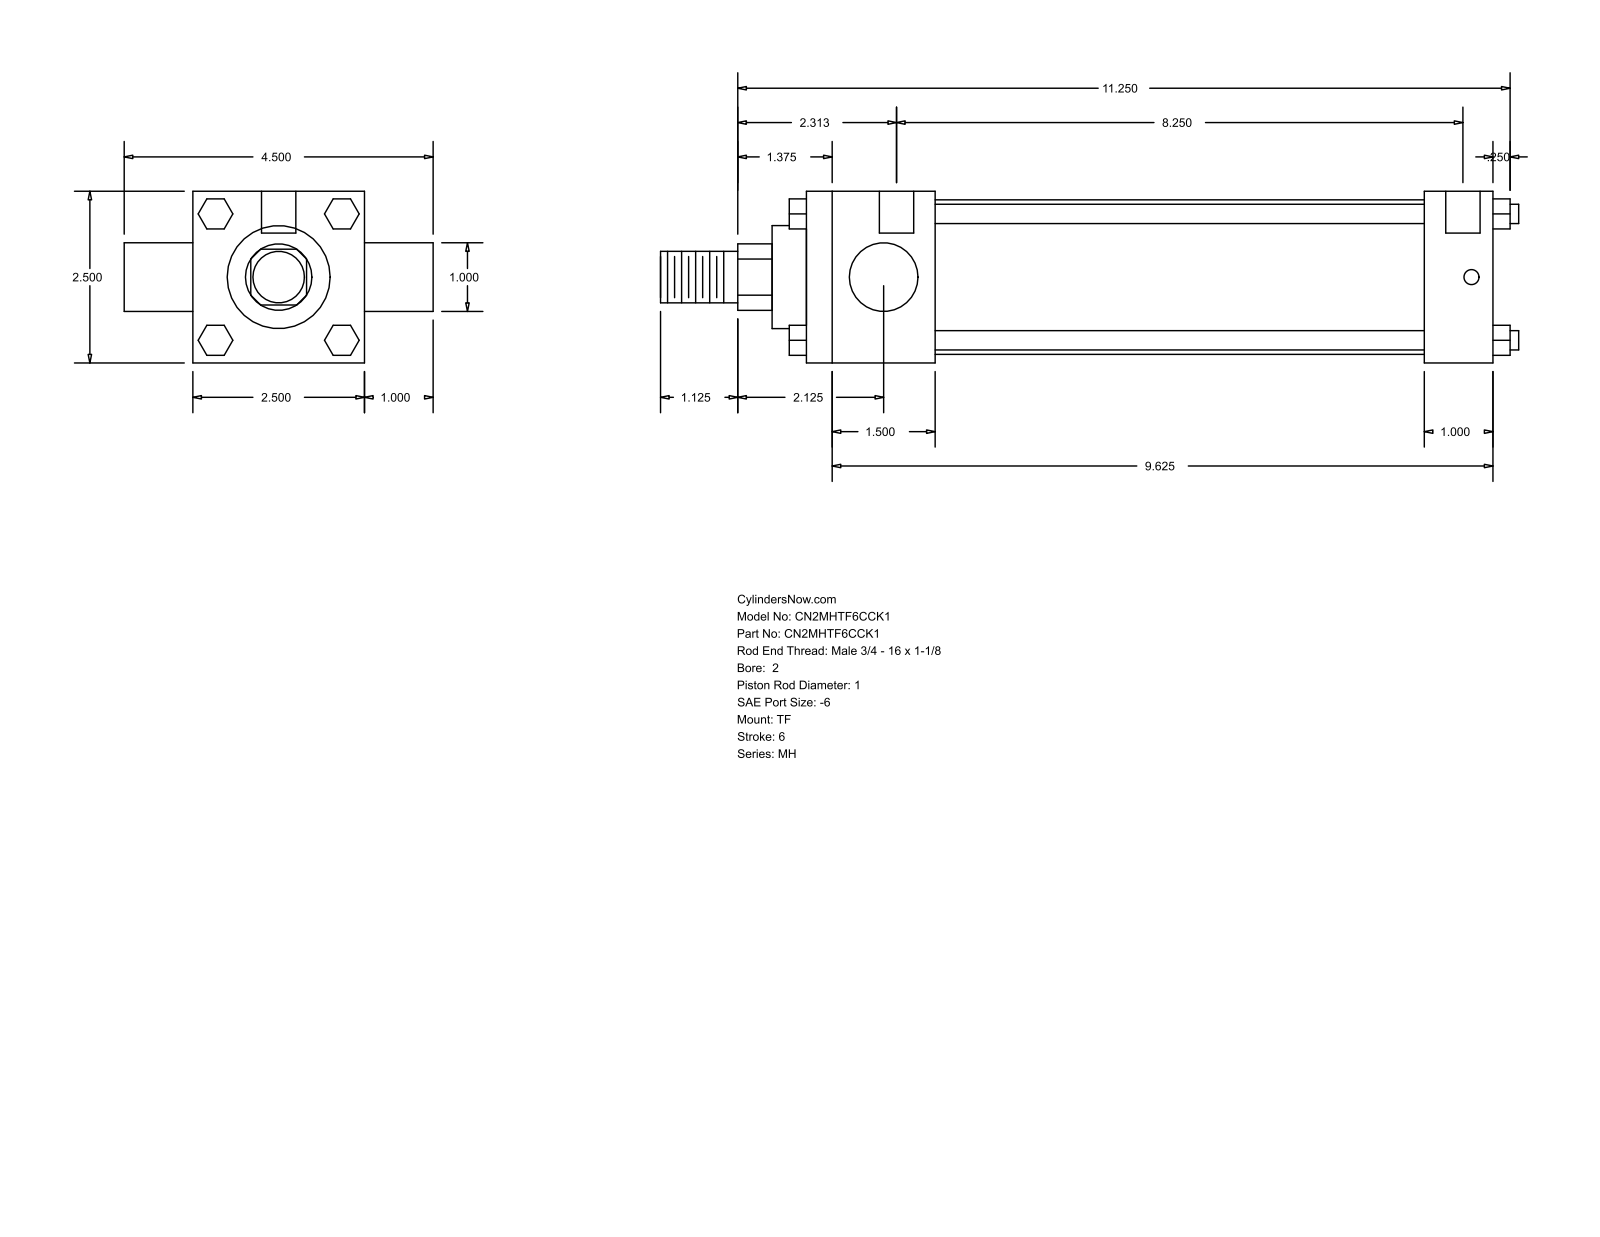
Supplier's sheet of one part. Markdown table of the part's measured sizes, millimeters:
| quantity | value |
| --- | --- |
| part name | MH_TF__0200_1 |
| STEP written by | GSSL Pune (CONFIG_CONTROL_DESIGN) |
| units | millimeters |
| bodies | 0 solids, 120 faces (92 planar, 28 cylindrical, 0 other) |
| overall size | 317.5 × 114.3 × 63.5 |
| round holes (diameter × count) | 5.56 × 3, 12.7 × 2 |
| round bosses / shafts (diameter × count) | 7.14 × 4, 25.4 × 2, 57.15 × 1, 38.1 × 1, 19.05 × 1 |
| partial cylindrical surfaces (radius × count) | 12.29 × 1 |
| main face-to-face distances | 63.5, 254, 25.4, 47.63, 228.6, 180.97, 206.37, 88.9, 266.7, 6.35 |
| hole center spacings | 3.17, 4.76, 209.55, 212.72, 214.31, 217.48 |
